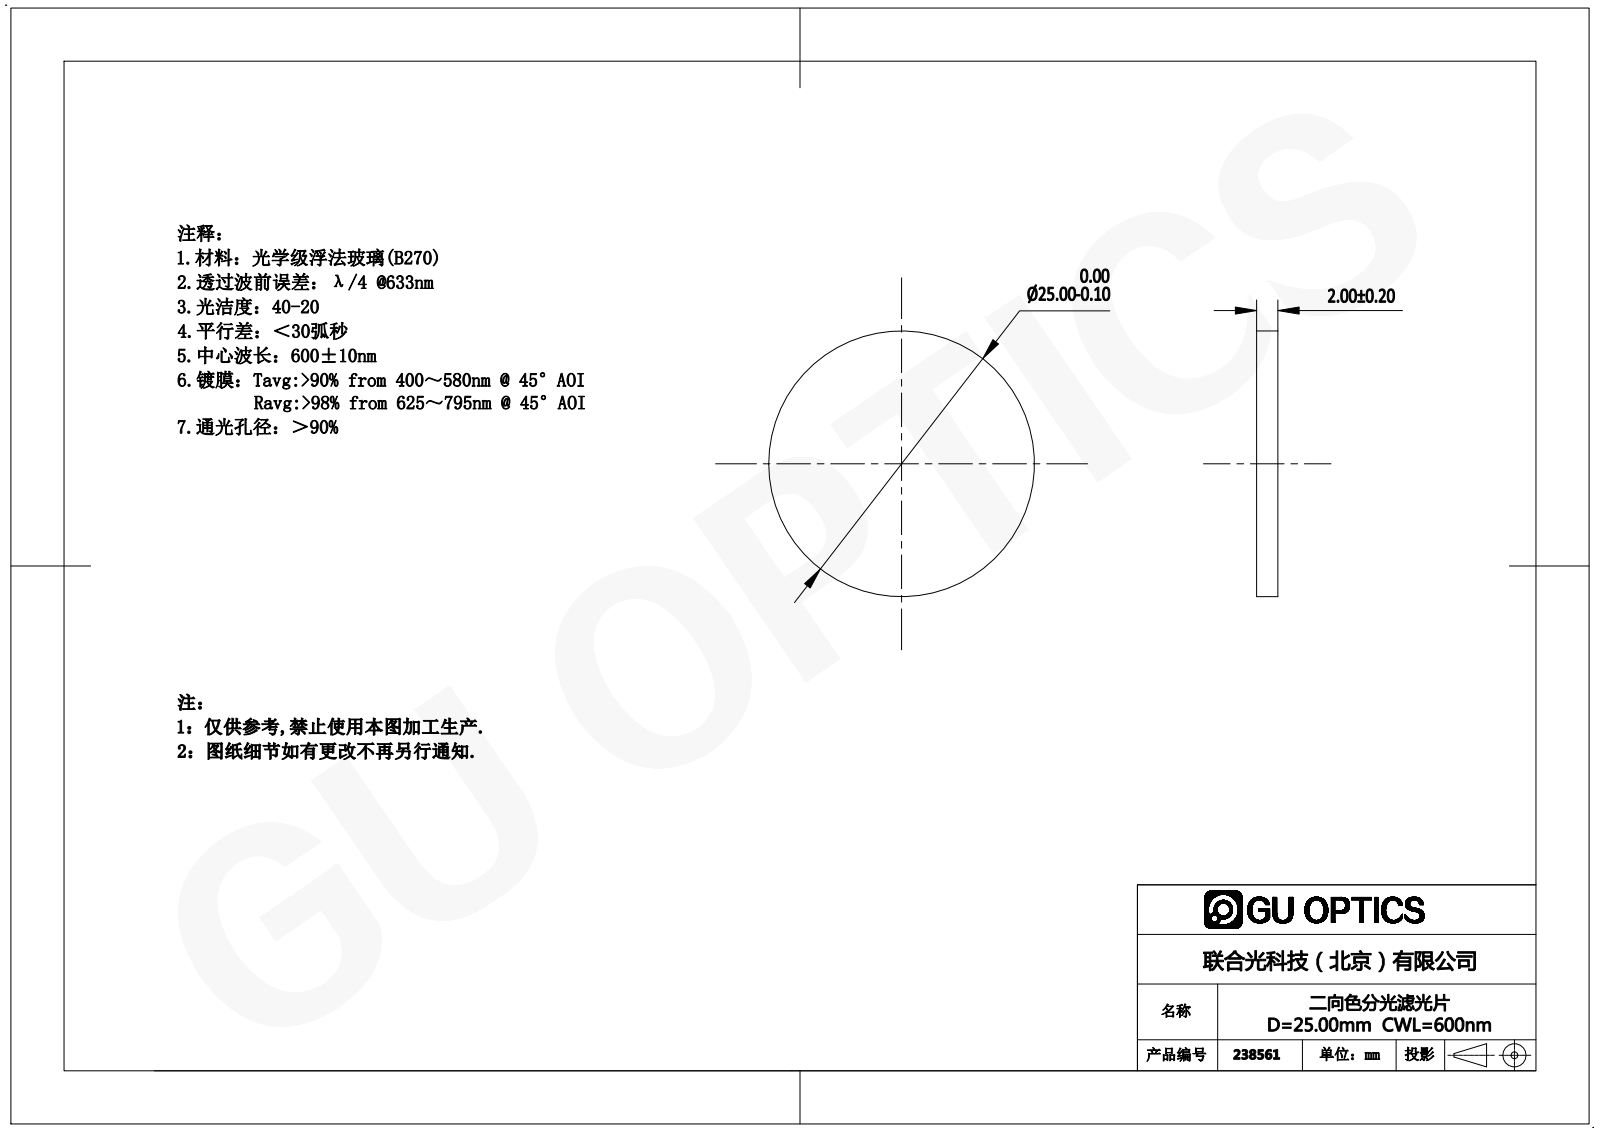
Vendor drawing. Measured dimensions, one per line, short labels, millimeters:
name: 238558
written by: SolidWorks 2016 (AUTOMOTIVE_DESIGN)
unit: mm
bodies: 1 solid, 4 faces (2 planar, 2 cylindrical, 0 other)
size: 25 × 25 × 2
volume: 982 mm³; area: 1 139 mm²
bosses: 1× ⌀25
face distances: 2
